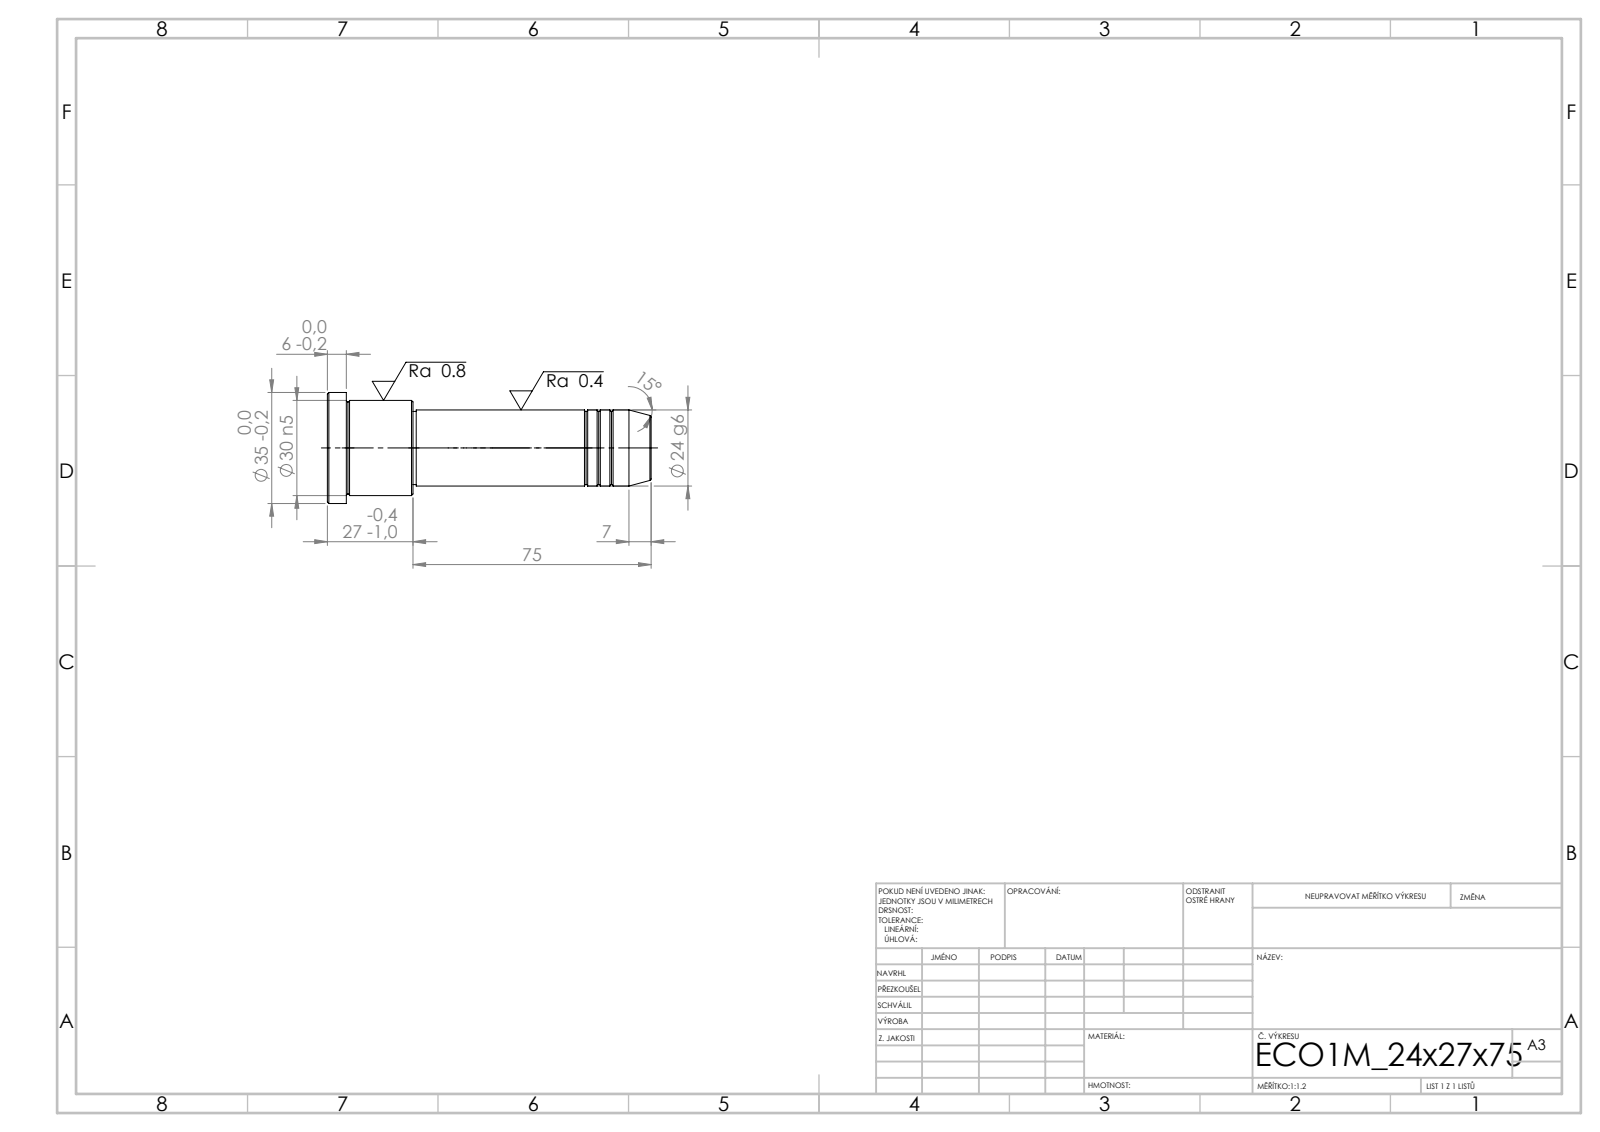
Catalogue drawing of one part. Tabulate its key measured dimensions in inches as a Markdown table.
| quantity | value |
| --- | --- |
| STEP written by | SolidWorks 2019 (CONFIG_CONTROL_DESIGN) |
| units | inches |
| bodies | 1 solid, 43 faces (5 planar, 14 cylindrical, 24 other) |
| overall size | 4.016 × 1.378 × 1.378 |
| volume | 3.289 in³ |
| surface area | 15.87 in² |
| round bosses / shafts (diameter × count) | 1.378 × 1, 1.181 × 1, 0.945 × 1, 0.906 × 1 |
| main face-to-face distances | 4.016, 3.78, 0.236, 2.953, 0.827, 1.063, 2.913, 0.039, 0.866, 1.102 |
